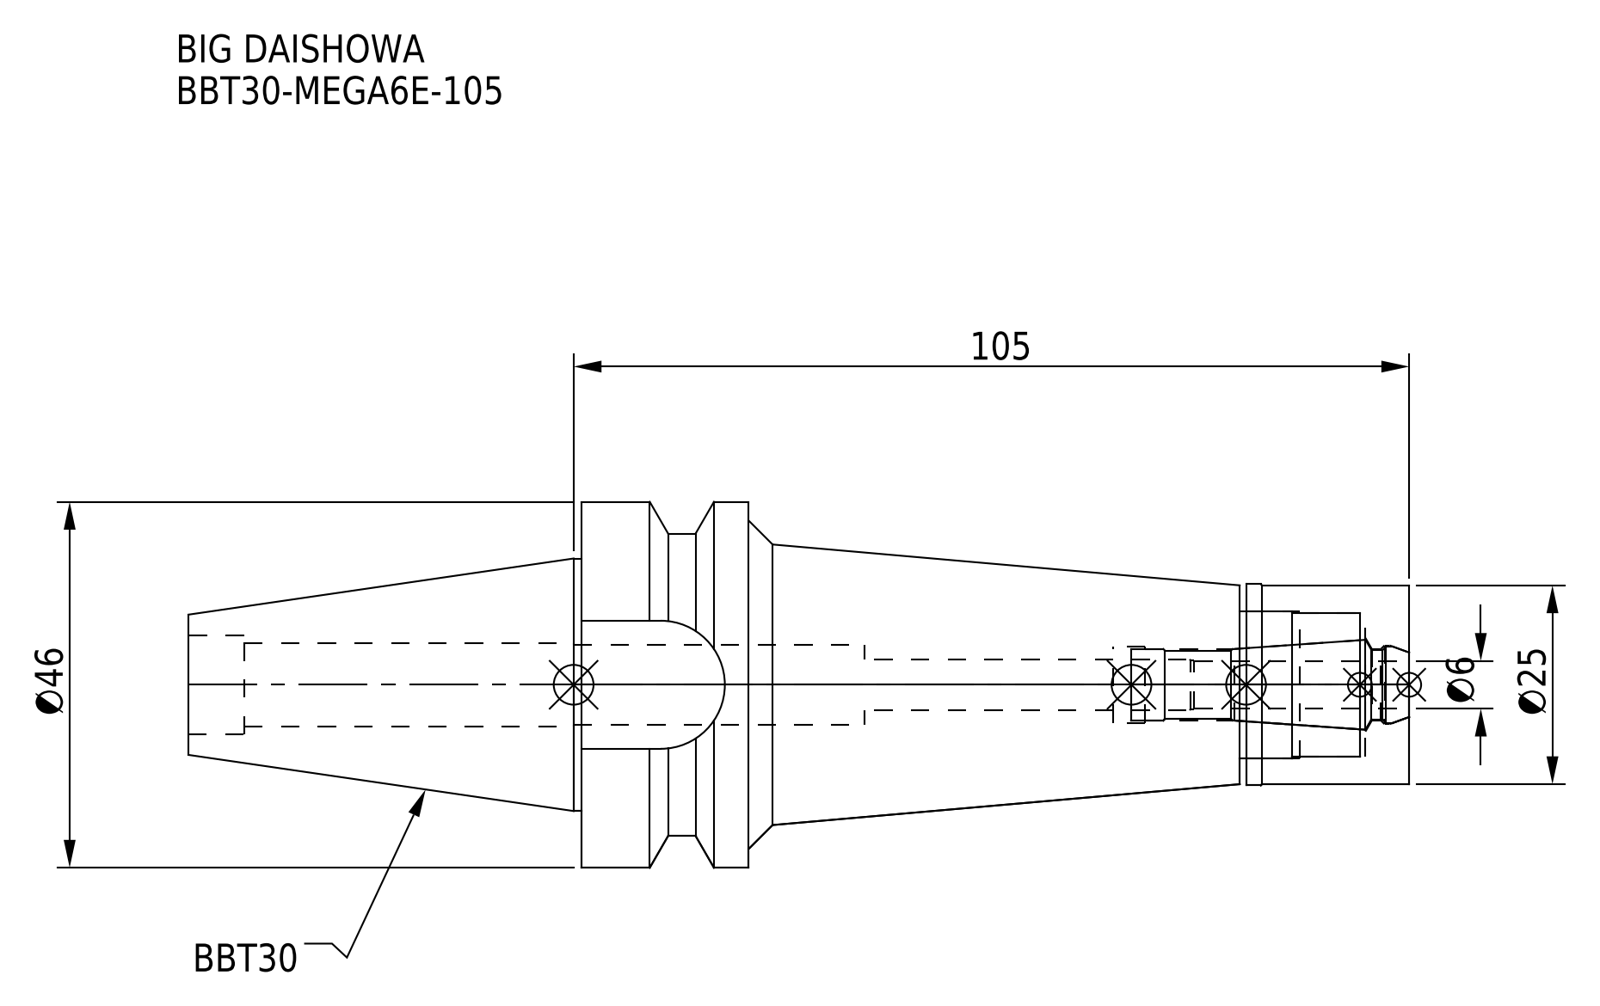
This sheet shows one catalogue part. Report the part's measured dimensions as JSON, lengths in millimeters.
{"part_name": "BBT30-MEGA6E-105-060-FreeParts; BBT30-MEGA6E-105-060.stp; BBT30-MEGA6E-105_1.stp; BBT30ME06105-060_ASM.stp (+3 more)", "step_written_by": "SolidWorks 2019 (CONFIG_CONTROL_DESIGN)", "units": "millimeters", "bodies": {"solids": 2, "faces": 79, "planar": 21, "cylindrical": 38, "other": 20}, "overall_size": [153.4, 46, 46], "volume_mm3": 98765, "surface_area_mm2": 24105, "round_holes": [[6.4, 1], [9, 1], [9.6, 1], [9.9, 1], [10, 1], [10.4, 1], [12.5, 1], [18, 1], [18.5, 1]], "round_bosses_or_shafts": [[46, 1], [31.75, 1], [25.3, 1], [25, 1]], "partial_cylinders_radius": [[8.05, 1], [19, 1]], "face_to_face_distances": [104, 83, 21, 32.6, 20.5, 62.5, 83.5, 21.3, 0.8, 61.7]}
